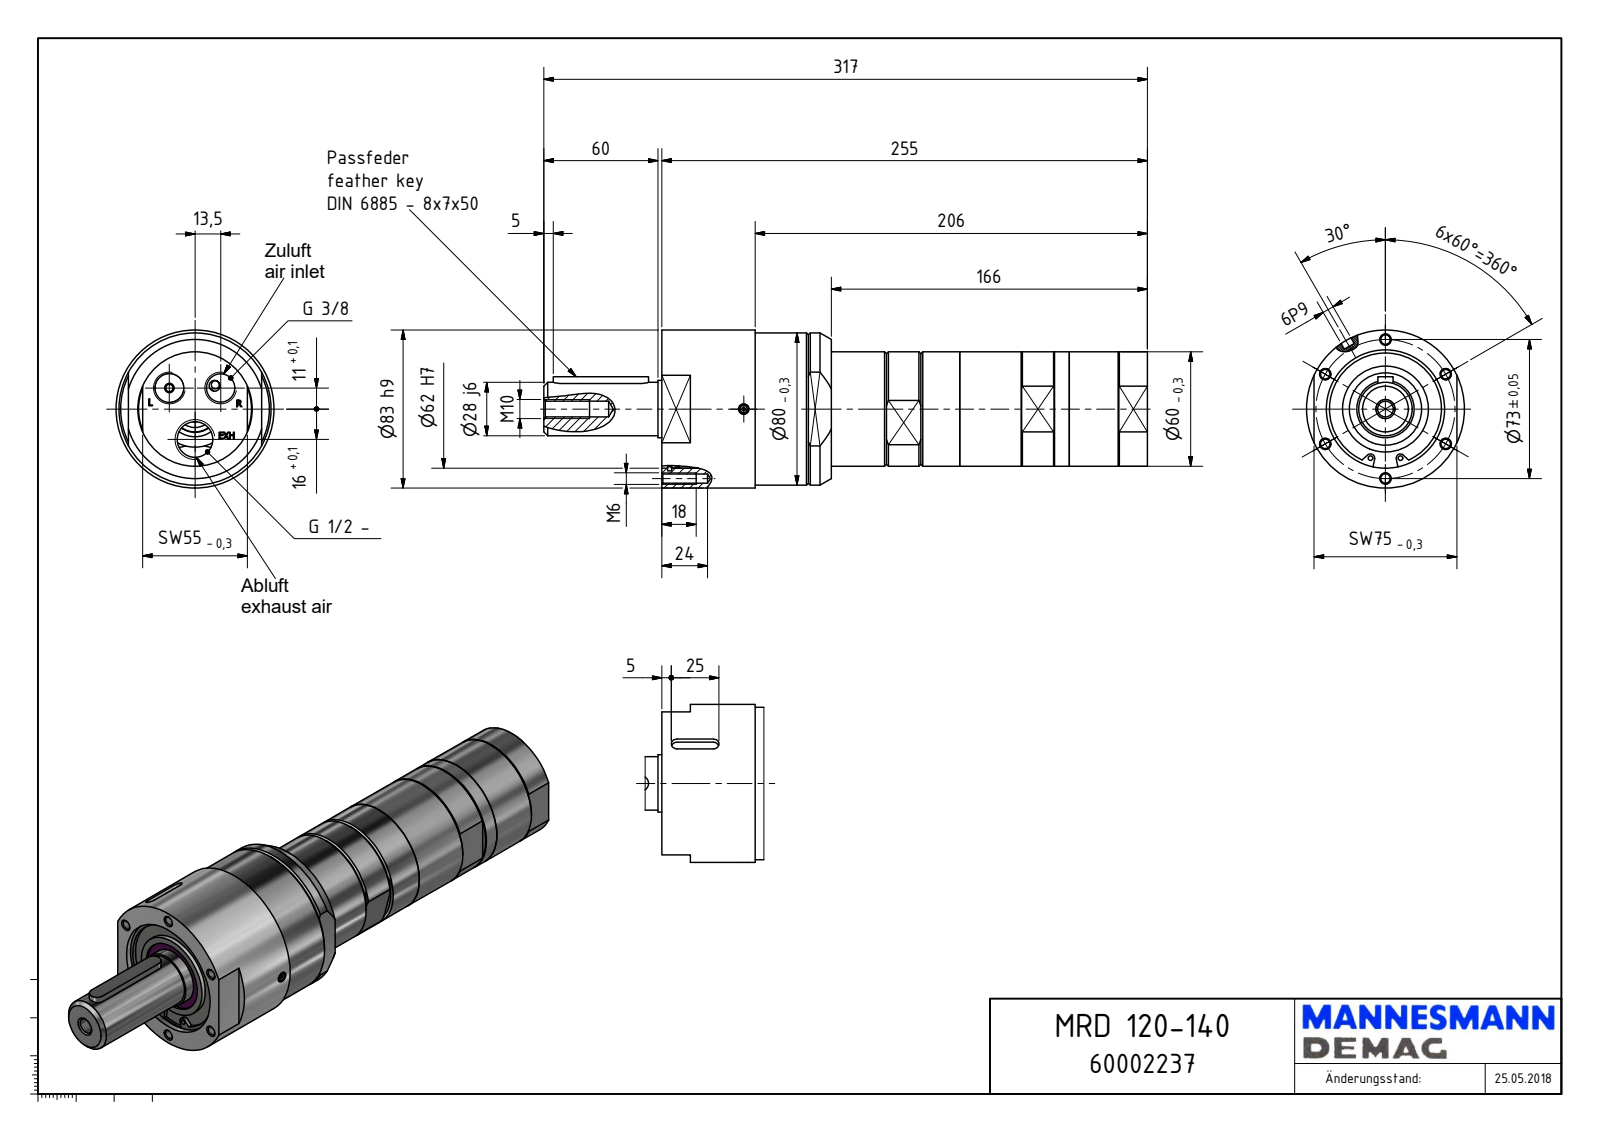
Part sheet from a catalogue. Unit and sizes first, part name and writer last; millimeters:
Units: millimetres
Overall size (bounding box): 317 × 83 × 83
Round holes (diameter × count): ⌀4.92 ×6, ⌀1.55 ×3, ⌀4 ×3, ⌀2.5 ×2, ⌀5.5 ×2, ⌀14.95 ×2, ⌀8.38 ×1, ⌀18.63 ×1, ⌀36.5 ×1, ⌀38 ×1, ⌀40 ×1, ⌀58.69 ×1
Round bosses / shafts (diameter × count): ⌀5 ×2, ⌀3.6 ×2, ⌀83 ×1, ⌀80 ×1, ⌀67 ×1, ⌀60 ×1, ⌀45 ×1, ⌀30 ×1
Partial cylindrical surfaces — rounded edges, fillets, slot ends (radius × count): R3.5 ×94, R2.25 ×2, R3 ×2, R4 ×2, R7.5 ×2, R8.5 ×1, R19.22 ×1, R23.5 ×1
Main face-to-face distances: 255, 2.5, 166, 65, 5, 89, 84, 250, 10, 55
Hole centre spacings: 36.5, 63.22, 73, 12.58, 13.29, 17.41, 19.51, 24.9
Volume: 937 066 mm³ · Surface area: 85 837 mm²
Bodies: 1 solid, 577 faces (237 planar, 269 cylindrical, 71 other)
Part name (STEP PRODUCT): MRD 120-140_60002237
STEP written by: Autodesk Inventor 2018 (AUTOMOTIVE_DESIGN)
